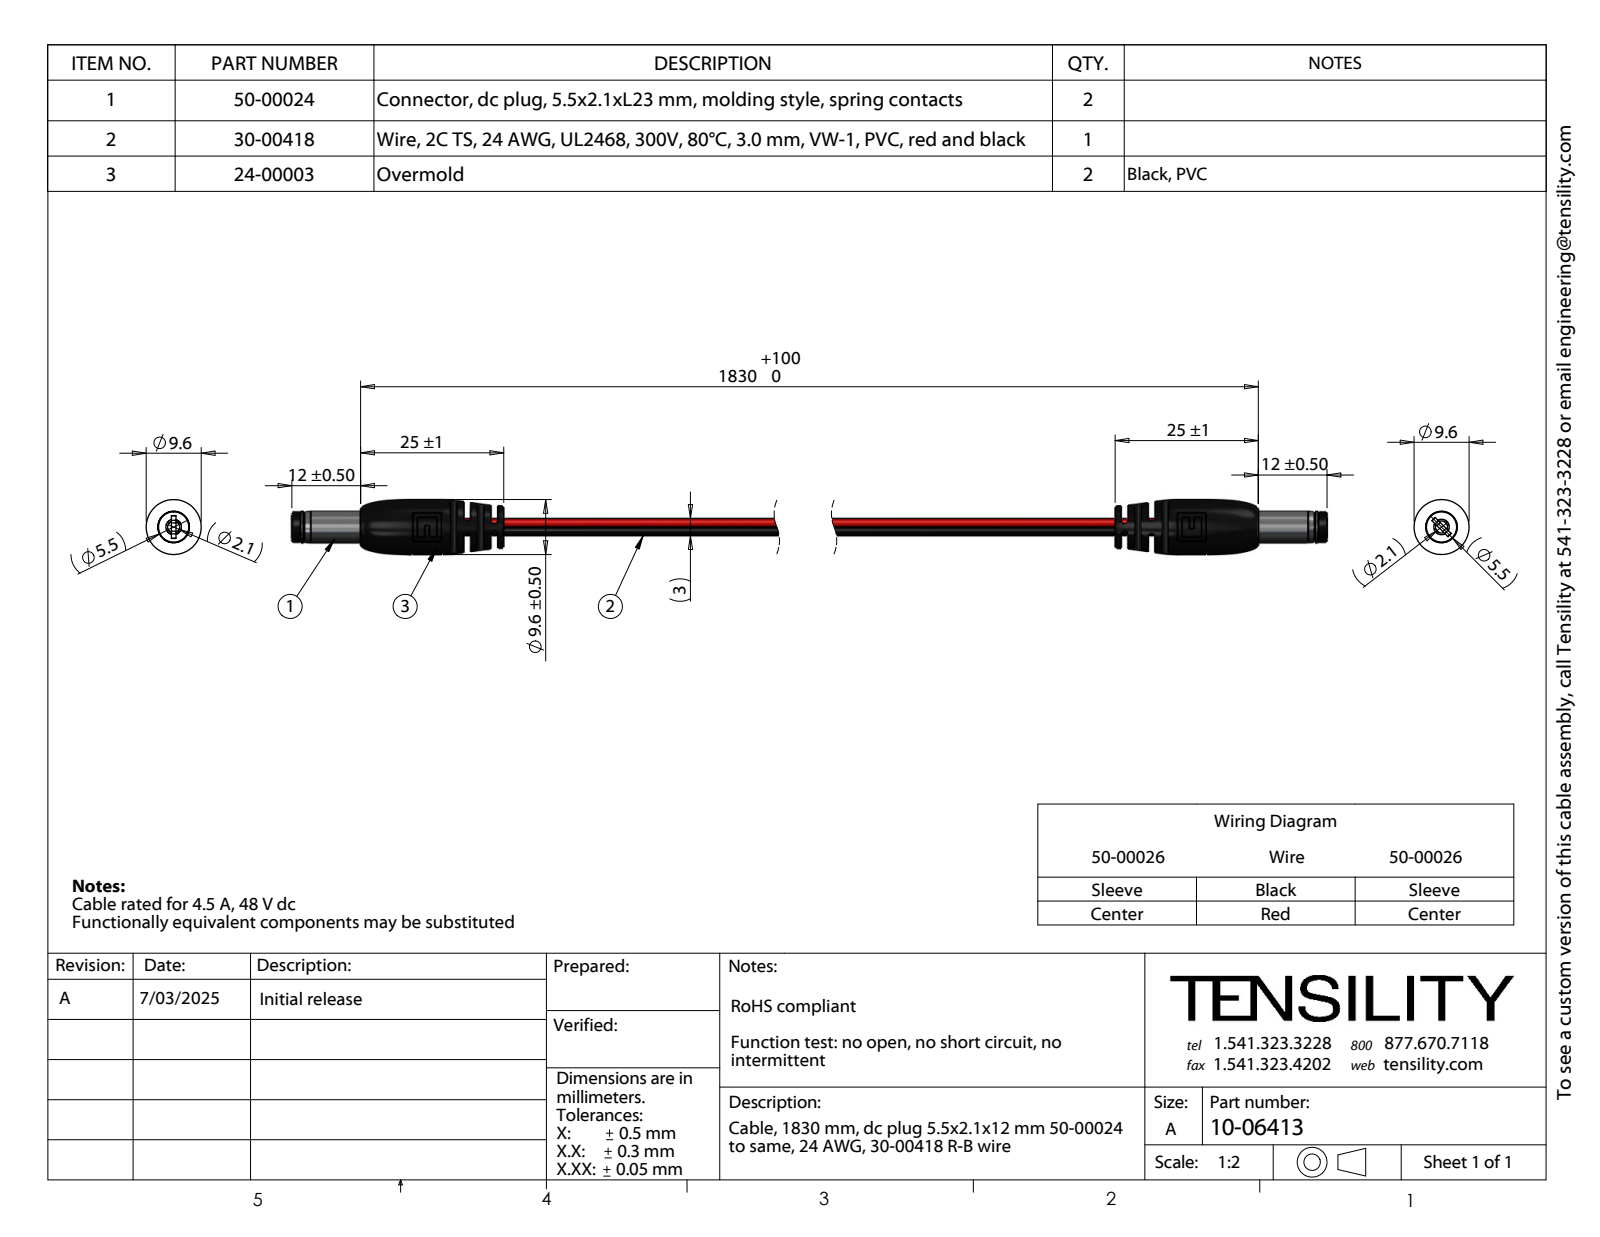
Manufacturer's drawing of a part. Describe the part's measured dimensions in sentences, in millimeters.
The part is named "30-00418_blunt cut; 50-00024 contact; 50-00024 insulator; 24-00003 (+3 more)". Its 3-D file was written by "SolidWorks 2025 (CONFIG_CONTROL_DESIGN)". It is 31 solids with 704 faces: 200 planar, 222 cylindrical and 282 other. Overall it measures 205.36 by 9.6 by 9.6 millimeters. Its volume is 3 682 cubic millimeters and its surface area 9 517 square millimeters. Round holes: 1 of diameter 2.1, 1 of diameter 4.79. Round bosses or shafts: 1 of diameter 9.6, 1 of diameter 5.5, 1 of diameter 5.3, 1 of diameter 4.8. Partial cylindrical surfaces (rounded edges, fillets, slot ends): 16 of radius 0.59, 8 of radius 0.15, 8 of radius 0.15, 4 of radius 0.1, 4 of radius 0.2, 4 of radius 0.21, 4 of radius 0.3, 4 of radius 0.4. The main face-to-face distances are 1.18, 2.36, 3.54, 4.72, 141.74, 0.8, 142.92, 140.56, 144.1, 5.9. The hole center spacings are 0.31, 0.35, 1.45, 0.32, 0.36, 0.43, 0.51, 1.46.
